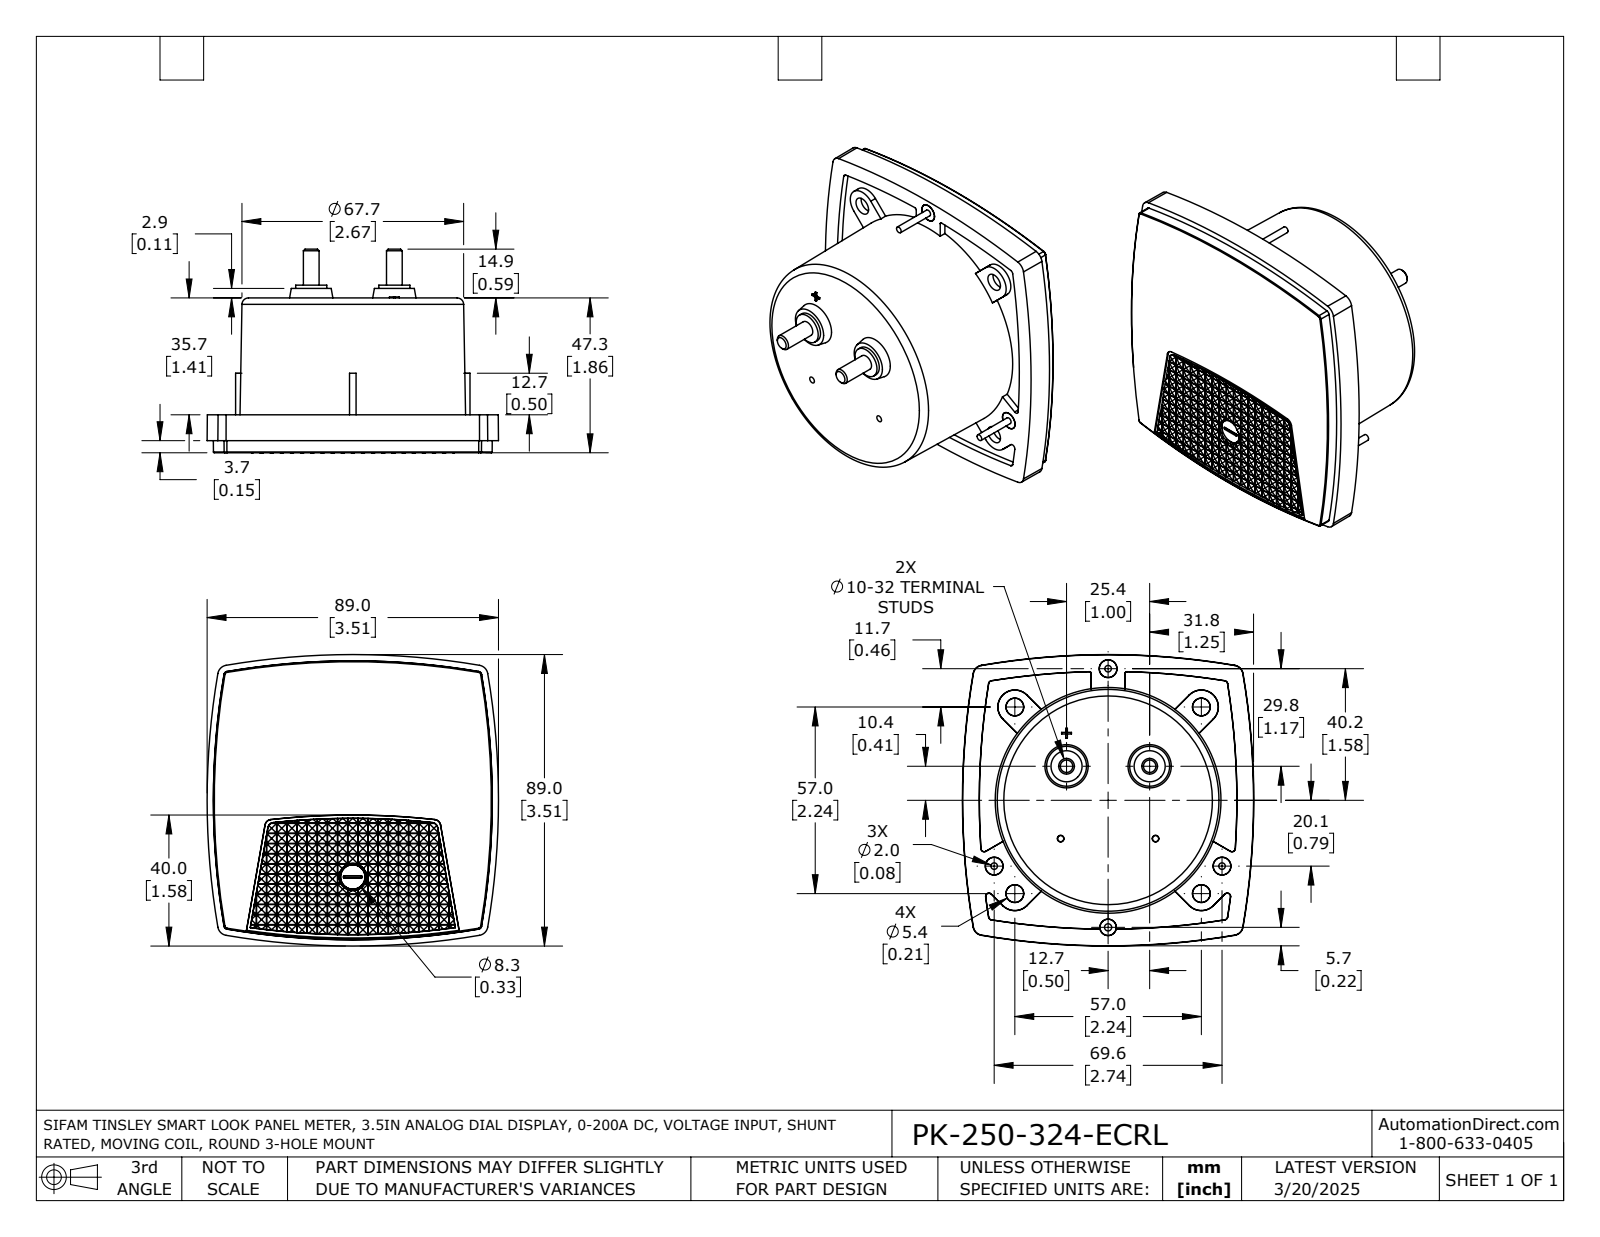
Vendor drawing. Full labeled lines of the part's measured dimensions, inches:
Part name (STEP PRODUCT): PK-250-324-ECRL
STEP written by: SolidWorks 2021 (AUTOMOTIVE_DESIGN)
Units: inches
Bodies: 1 solid, 1078 faces (950 planar, 23 cylindrical, 105 other)
Overall size (bounding box): 3.505 × 3.505 × 2.453
Volume: 12.99 in³ · Surface area: 44.29 in²
Round holes (diameter × count): ⌀0.087 ×1
Round bosses / shafts (diameter × count): ⌀0.213 ×3, ⌀0.079 ×3, ⌀0.374 ×2, ⌀0.189 ×2
Partial cylindrical surfaces — rounded edges, fillets, slot ends (radius × count): R8.961 ×1
Main face-to-face distances: 1.862, 1.406, 0.457, 0.079, 1.484, 0.378, 0.024, 0.096, 0.072, 0.12
